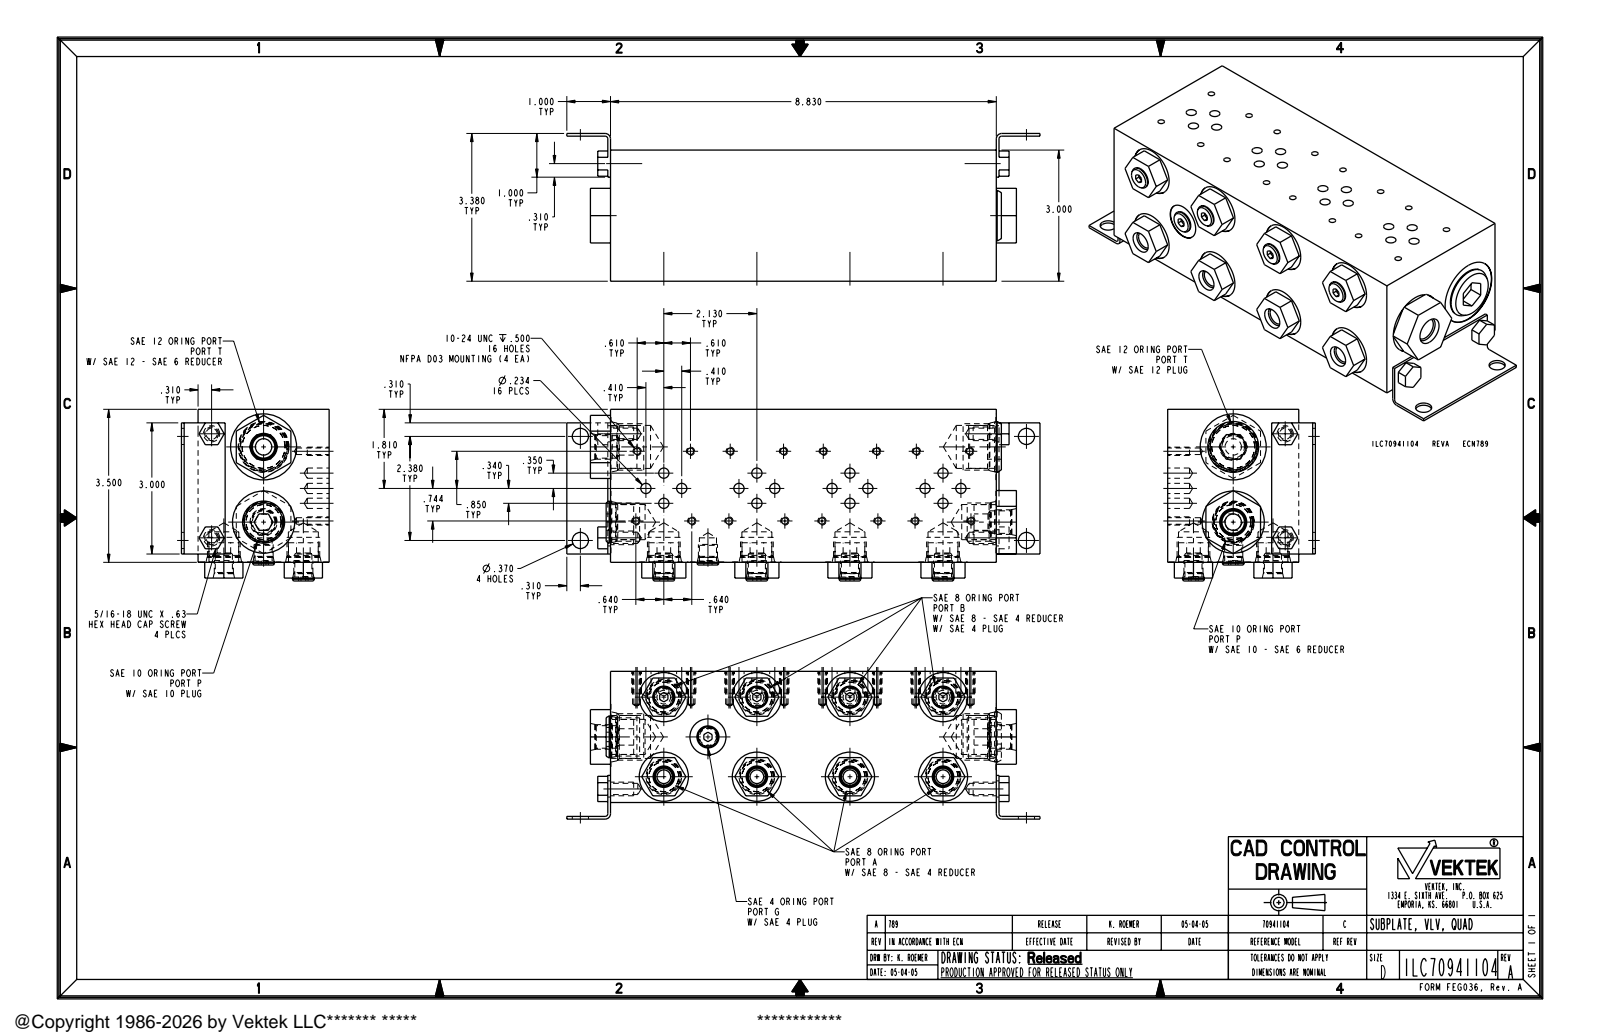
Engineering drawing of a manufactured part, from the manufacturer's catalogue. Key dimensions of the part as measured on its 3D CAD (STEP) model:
Part name (STEP PRODUCT): ILC70941104
STEP written by: PRO/ENGINEER BY PARAMETRIC TECHNOLOGY CORPORATION, 2004290 (AUTOMOTIVE_DESIGN_CC2)
Units: inches
Bodies: 8 solids, 823 faces (277 planar, 308 cylindrical, 238 other)
Overall size (bounding box): 10.83 × 3.927 × 3.38
Volume: 92.97 in³ · Surface area: 276.5 in²
Round holes (diameter × count): ⌀0.15 ×16, ⌀0.19 ×16, ⌀0.234 ×16, ⌀0.392 ×9, ⌀0.312 ×8, ⌀0.686 ×8, ⌀1.125 ×8, ⌀0.37 ×6, ⌀0.257 ×2, ⌀0.313 ×2, ⌀0.375 ×2, ⌀0.515 ×2
Round bosses / shafts (diameter × count): ⌀0.75 ×8, ⌀0.68 ×8, ⌀0.437 ×8, ⌀0.39 ×5, ⌀0.563 ×2, ⌀1.063 ×1, ⌀0.98 ×1, ⌀0.875 ×1
Partial cylindrical surfaces — rounded edges, fillets, slot ends (radius × count): R0.062 ×2, R0.124 ×2
Main face-to-face distances: 3, 3.5, 0.062, 8.83, 0.38, 3.38, 0.318, 3.318, 0.36, 3.49
Hole centre spacings: 2.13, 4.26, 0.779, 1.287, 4.26, 0.873, 1.337, 1.594
